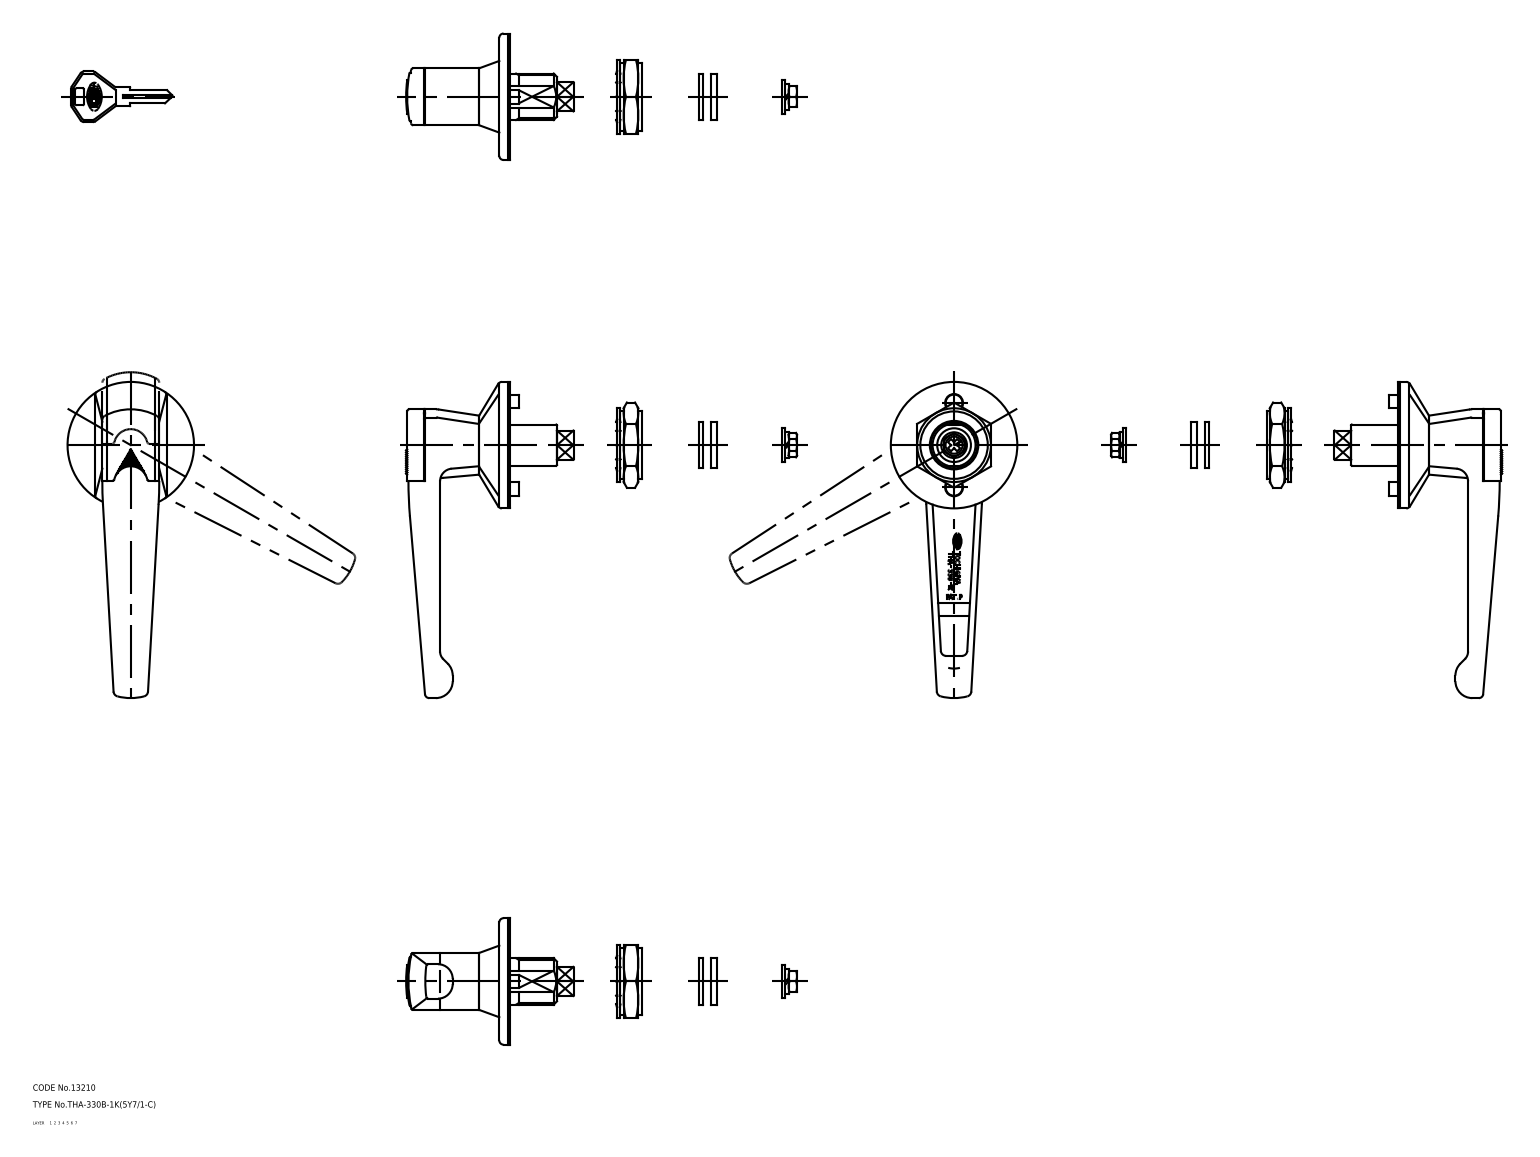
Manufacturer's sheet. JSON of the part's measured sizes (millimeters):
{"part_name": "washer_D; washer_C; washer_B; washer_A (+8 more)", "step_written_by": "CADfix (AUTOMOTIVE_DESIGN)", "units": "millimeters", "bodies": {"solids": 11, "faces": 349, "planar": 0, "cylindrical": 0, "other": 349}, "overall_size": [150, 138.84, 60], "volume_mm3": 85646, "surface_area_mm2": 41530}
